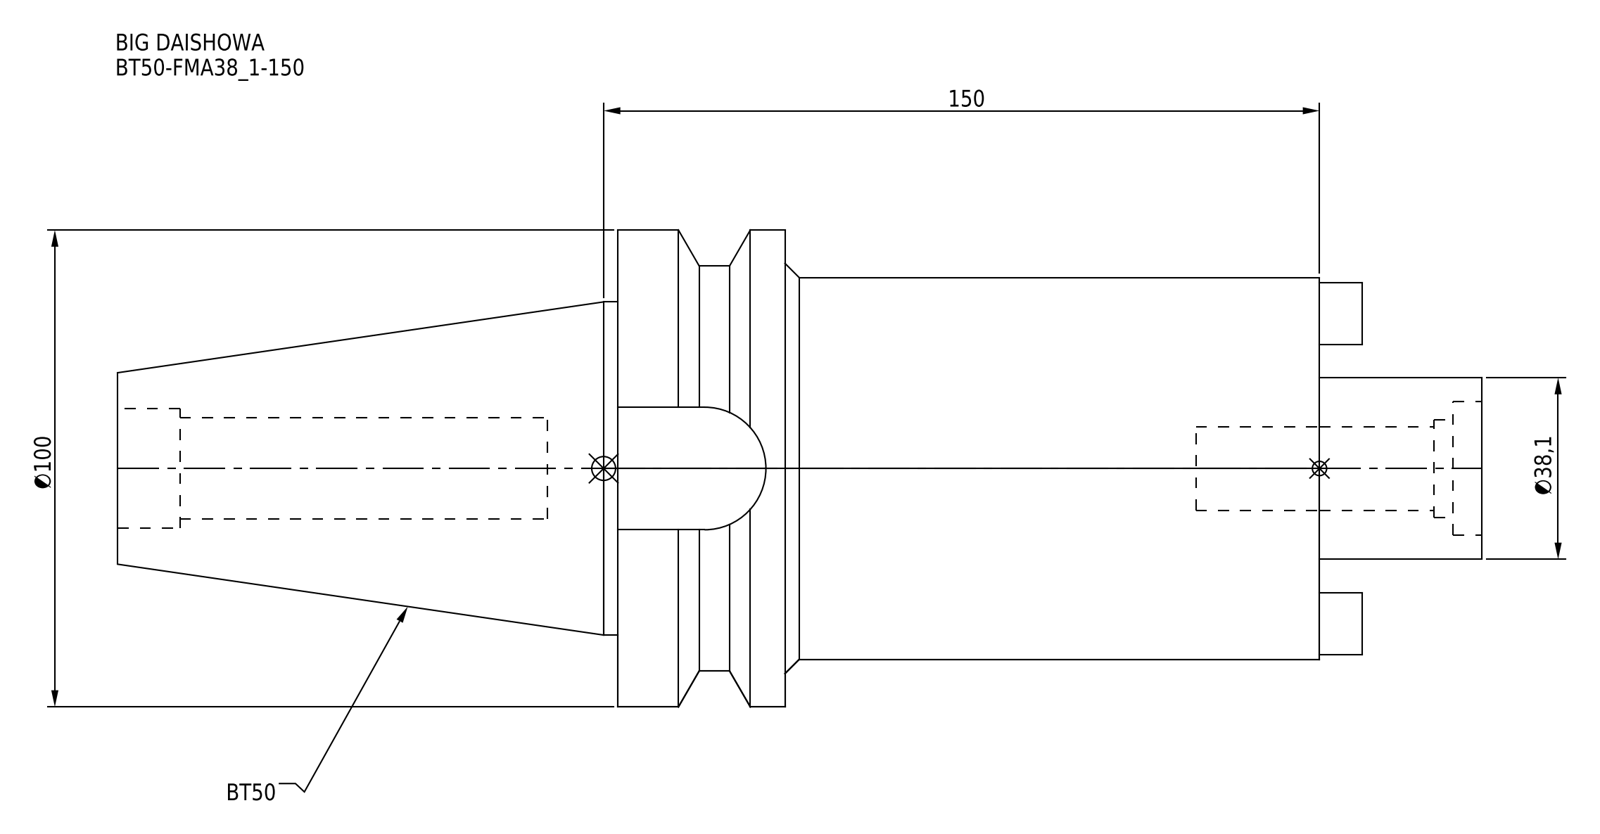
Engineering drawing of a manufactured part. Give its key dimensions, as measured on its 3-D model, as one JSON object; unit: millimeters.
{"part_name": "BT50-FMA38_1-150", "step_written_by": "CREO PARAMETRIC BY PTC INC, 2016380 (AUTOMOTIVE_DESIGN)", "units": "millimeters", "bodies": {"solids": 1, "faces": 60, "planar": 26, "cylindrical": 26, "other": 8}, "overall_size": [285.8, 100, 100], "volume_mm3": 1050000, "surface_area_mm2": 87643, "round_holes": [[17.5, 1], [20.5, 1], [21.2, 1], [25, 1], [28, 1]], "round_bosses_or_shafts": [[100, 1], [85, 1], [80, 1], [69.85, 1], [38.1, 1]], "partial_cylinders_radius": [[12.85, 1]], "face_to_face_distances": [147, 112, 35, 251.8, 139.8, 104.8, 70.8, 34, 146, 181]}
